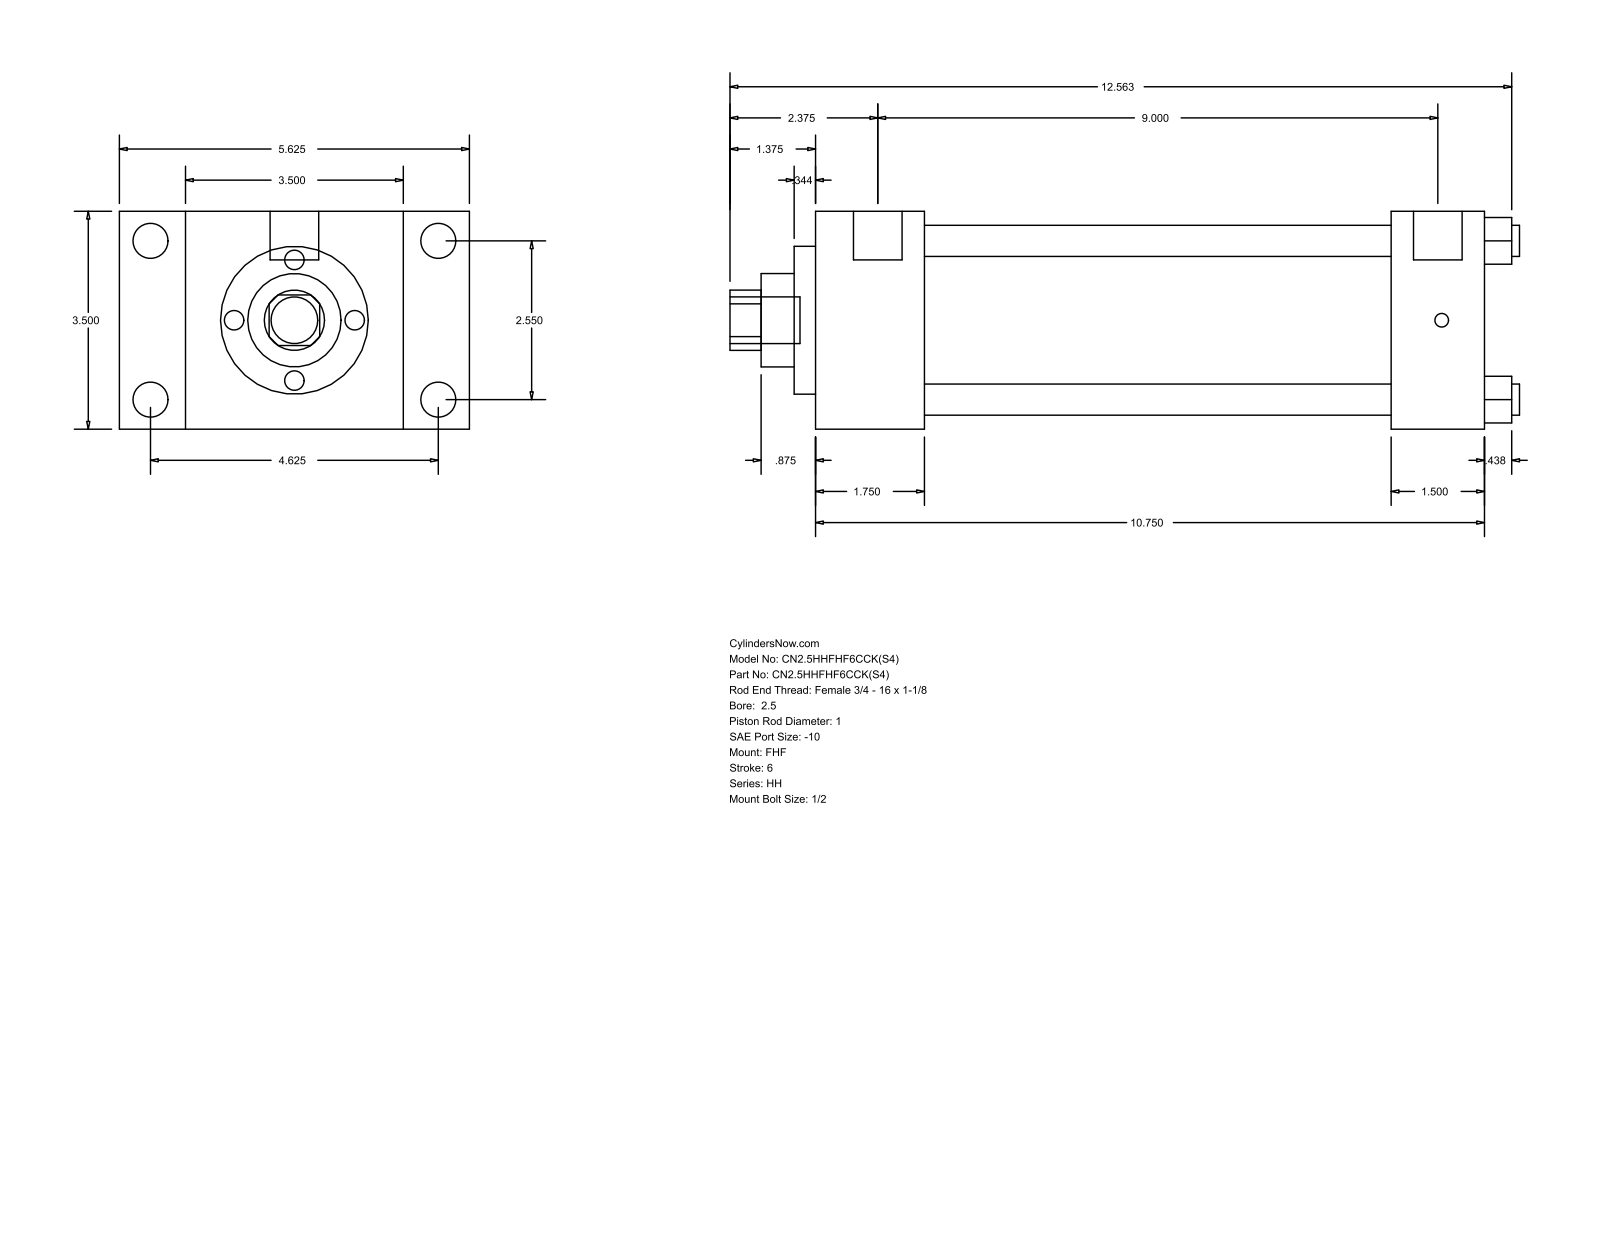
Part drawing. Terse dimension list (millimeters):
name: HH_FHF__0250_1
written by: GSSL Pune (CONFIG_CONTROL_DESIGN)
unit: mm
bodies: 0 solids, 90 faces (61 planar, 29 cylindrical, 0 other)
size: 322.26 × 142.88 × 88.9
holes: 4× ⌀12.7, 1× ⌀25.4, 1× ⌀38.1, 1× ⌀60.33, 1× ⌀73.03
bosses: 4× ⌀14.3, 4× ⌀5.56, 2× ⌀19.84, 1× ⌀19.05
rounds: 1× R12.29
face distances: 88.9, 44.46, 26.99, 115.89, 273.06, 228.6, 142.88, 234.96, 190.5, 38.1
hole spacings: 45.79, 64.76, 91.58
